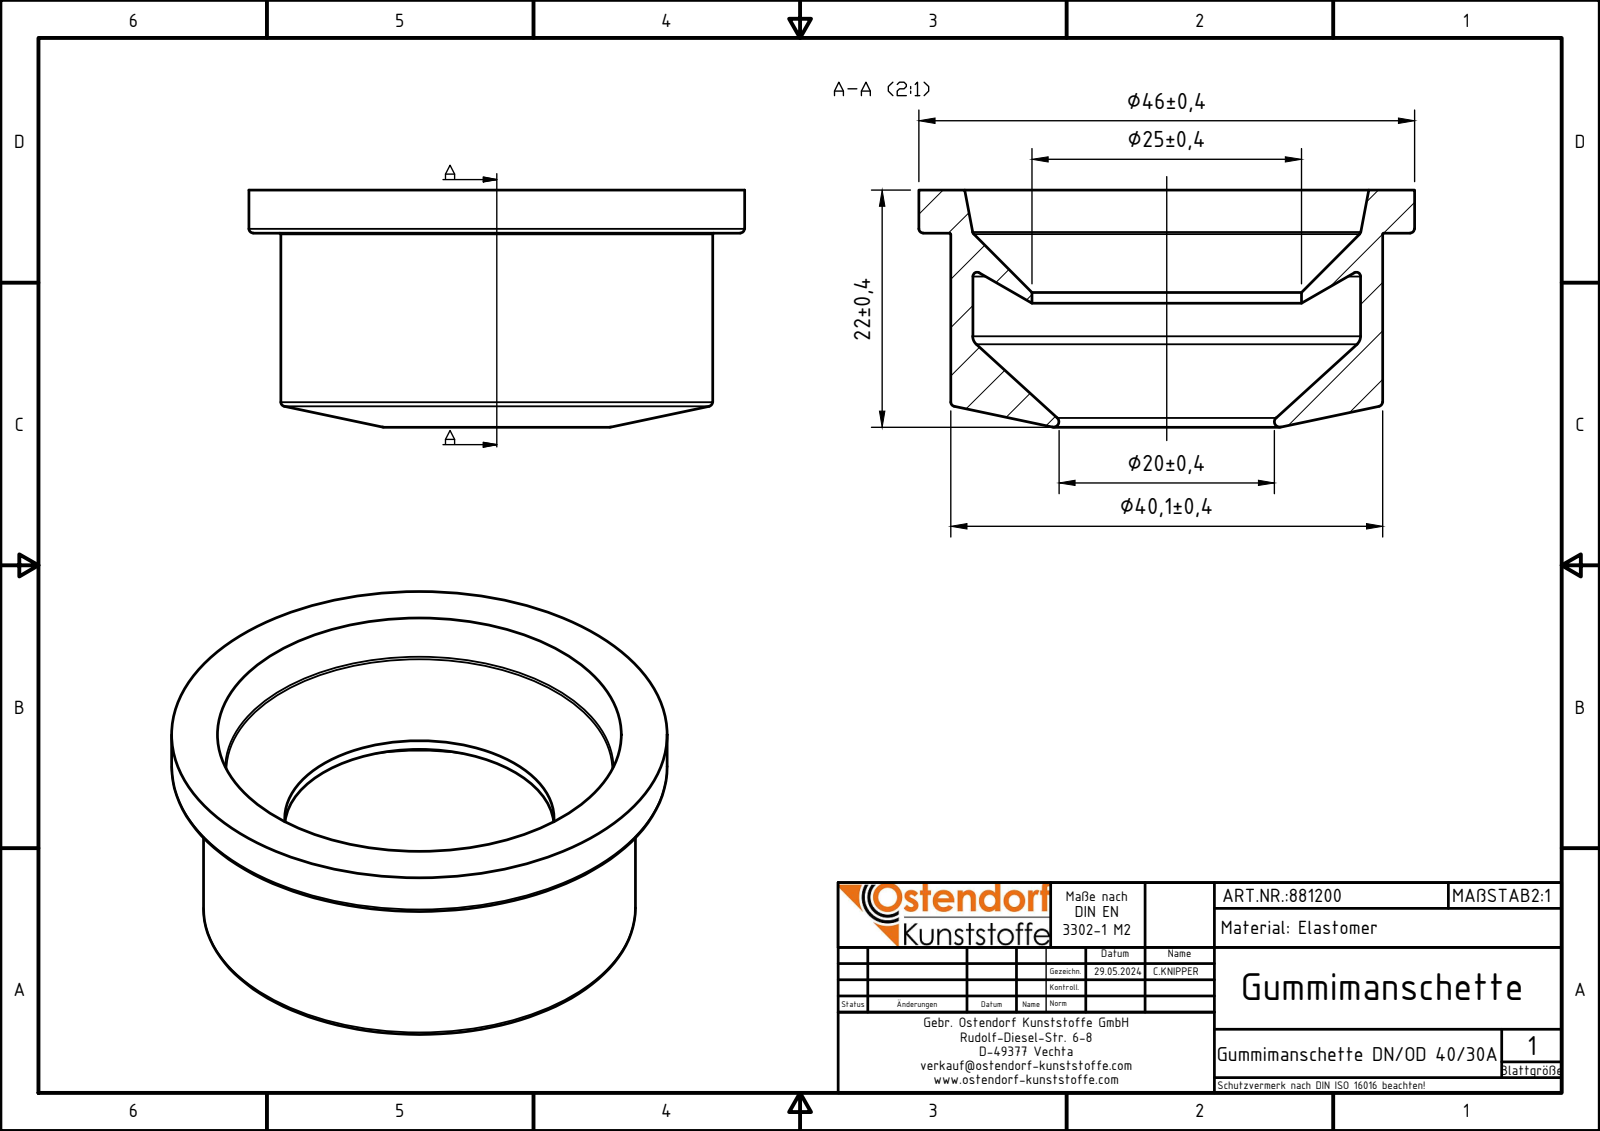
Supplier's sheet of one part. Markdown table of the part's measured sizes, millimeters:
| quantity | value |
| --- | --- |
| part name | 881200z |
| STEP written by | Autodesk Inventor 2024 (AUTOMOTIVE_DESIGN) |
| units | millimeters |
| bodies | 1 solid, 18 faces (2 planar, 4 cylindrical, 12 other) |
| overall size | 46 × 46 × 22 |
| volume | 10 301 mm³ |
| surface area | 8 046 mm² |
| round holes (diameter × count) | 25 × 1, 36 × 1 |
| round bosses / shafts (diameter × count) | 46 × 1, 40.1 × 1 |
| main face-to-face distances | 4 |
